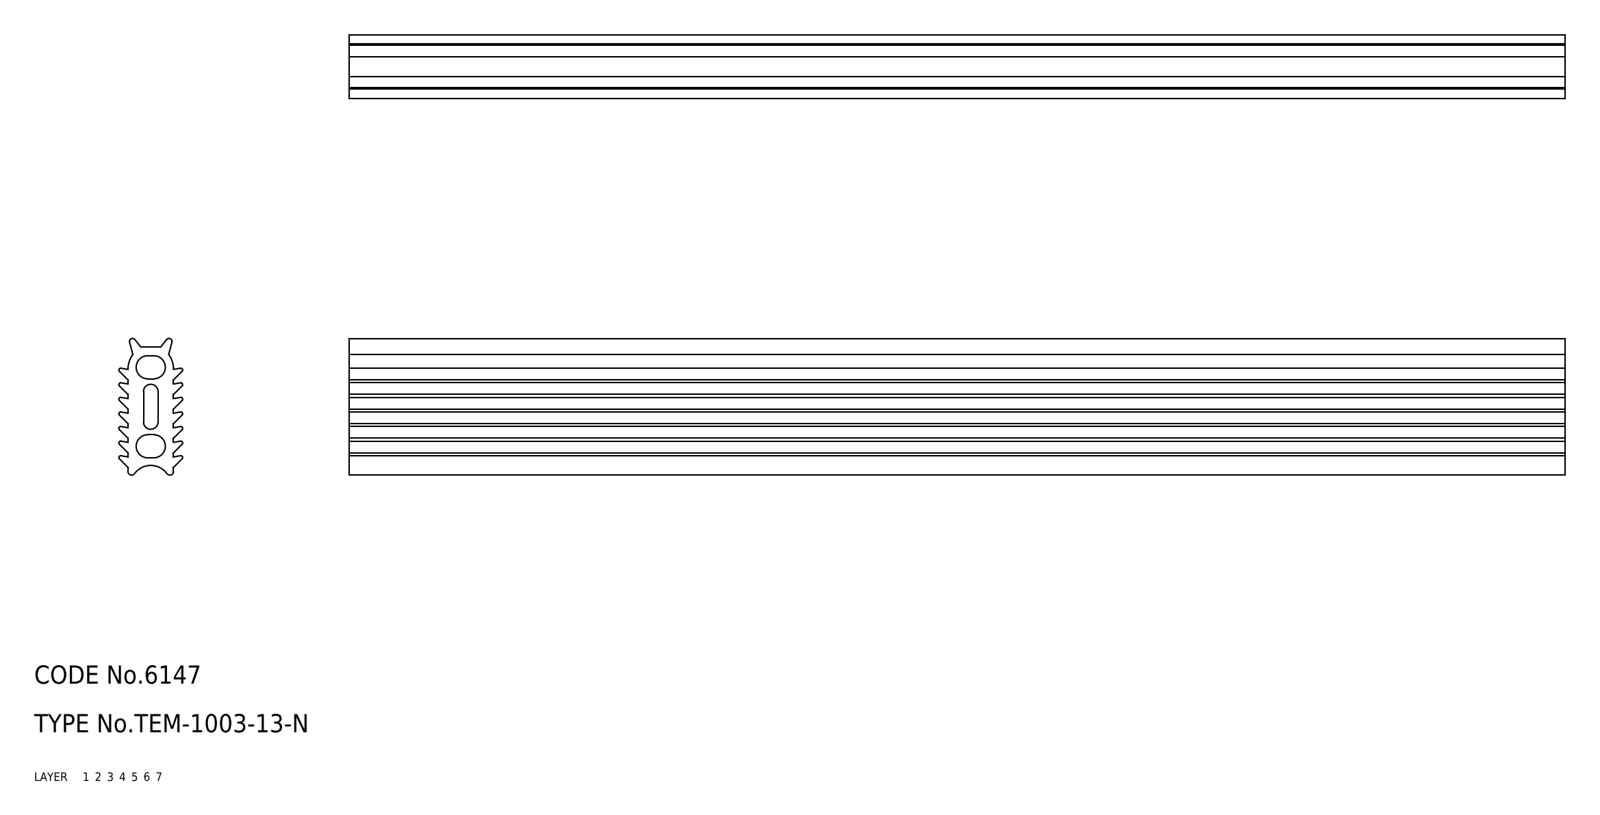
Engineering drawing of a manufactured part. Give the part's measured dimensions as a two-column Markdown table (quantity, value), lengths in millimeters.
| quantity | value |
| --- | --- |
| part name | gasket |
| STEP written by | CADfix (AUTOMOTIVE_DESIGN) |
| units | millimeters |
| bodies | 1 solid, 82 faces (0 planar, 0 cylindrical, 82 other) |
| overall size | 200 × 22.5 × 10.5 |
| volume | 25 610 mm³ |
| surface area | 27 762 mm² |
